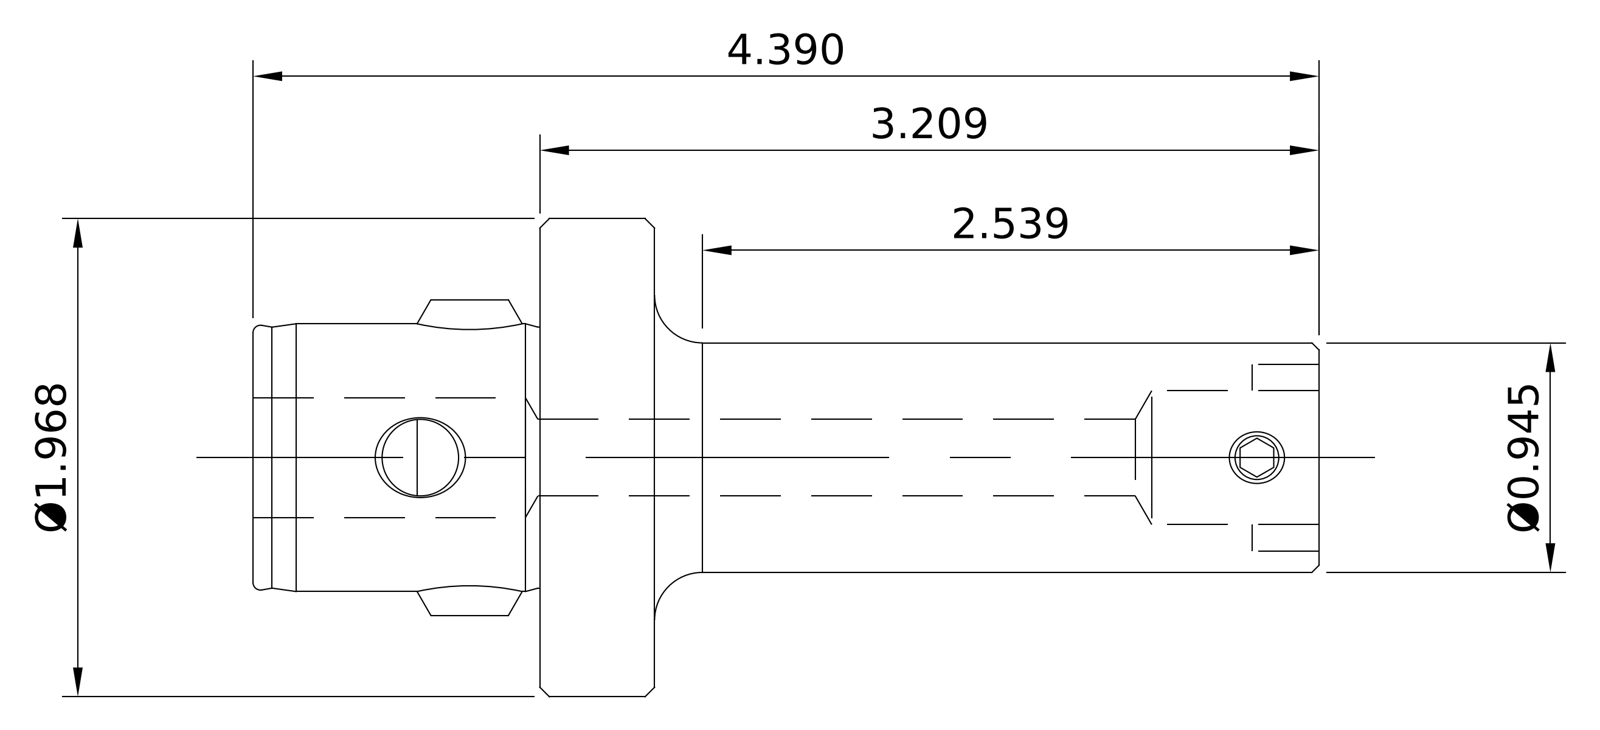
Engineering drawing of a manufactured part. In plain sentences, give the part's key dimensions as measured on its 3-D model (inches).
The part is named "10.691.50X_10.691.505; 10.332.520_11.332.520; 10.690.43X_10.690.432; 691-50XRing_10.691.505Ring (+1 more)". Its 3-D file was written by "SolidWorks 2016 (CONFIG_CONTROL_DESIGN)". It is 4 solids with 96 faces: 42 planar, 25 cylindrical and 29 other. Overall it measures 4.39 by 1.969 by 1.969 inches. Its volume is 3.807 cubic inches and its surface area 29.84 square inches. Round holes: 1 of diameter 0.165, 1 of diameter 0.177, 1 of diameter 0.205, 1 of diameter 0.315, 1 of diameter 0.346, 1 of diameter 0.394, 1 of diameter 0.433, 1 of diameter 0.492, 1 of diameter 0.551, 1 of diameter 0.571. Round bosses or shafts: 1 of diameter 1.969, 1 of diameter 1.102, 1 of diameter 0.945, 1 of diameter 0.429, 1 of diameter 0.272, 1 of diameter 0.197. Partial cylindrical surfaces (rounded edges, fillets, slot ends): 2 of radius 0.079, 1 of radius 0.551. The main face-to-face distances are 0.472, 1.181, 1.654, 4.39, 3.209, 2.736, 0.157, 0.866, 0.709, 0.433. The hole center spacings are 0.413, 3.443.
